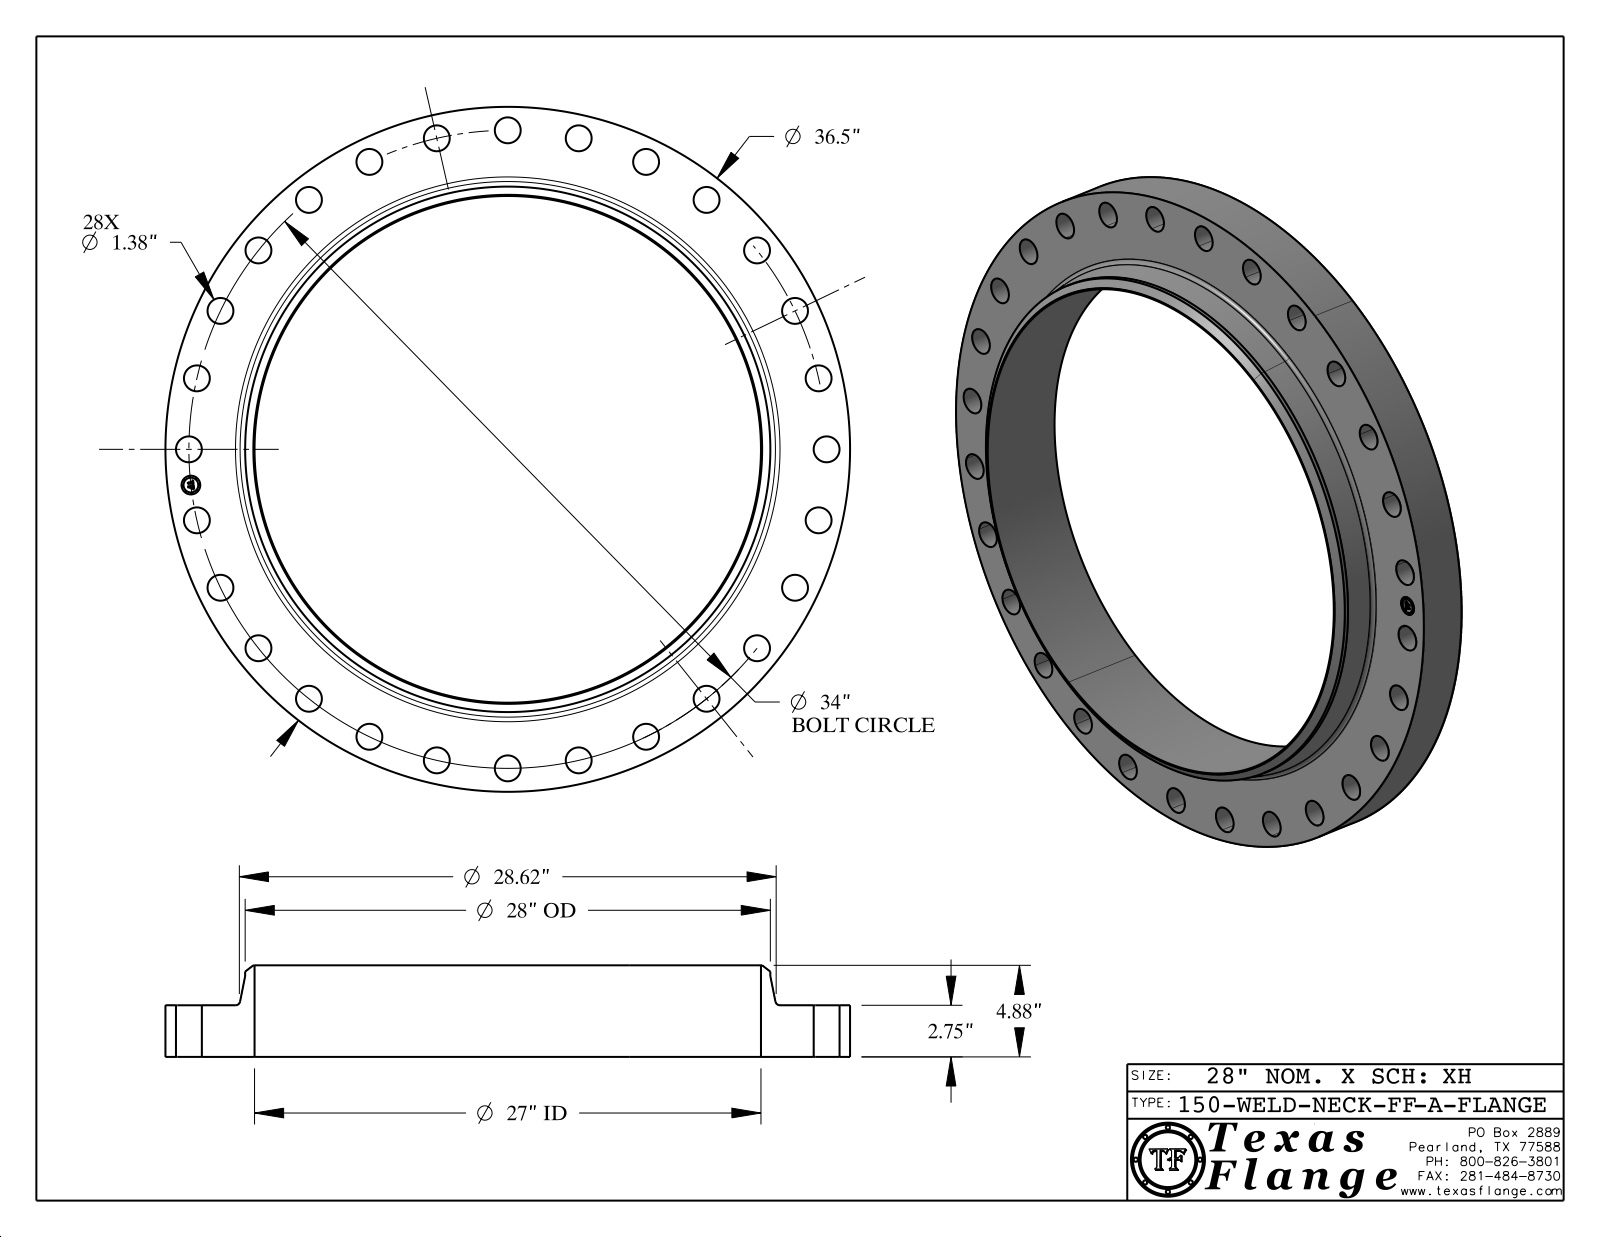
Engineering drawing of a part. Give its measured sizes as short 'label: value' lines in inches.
name: 150-WELD-NECK-FF, Series A
written by: CATIA V5 STEP AP214 (AUTOMOTIVE_DESIGN)
unit: in
bodies: 1 solid, 456 faces (368 planar, 82 cylindrical, 6 other)
size: 36.5 × 36.5 × 4.88
volume: 1 296 in³; area: 2 065 in²
holes: 28× ⌀1.38, 1× ⌀1, 1× ⌀27
bosses: 8× ⌀0.061, 1× ⌀36.5, 1× ⌀28, 1× ⌀0.788
face distances: 2.75, 4.88, 2.13, 0.015, 2.735, 2.145, 0.298, 0.293, 0.054, 0.193
hole spacings: 3.807, 7.566, 30.633, 33.786, 17, 11.23, 18.089, 21.198
